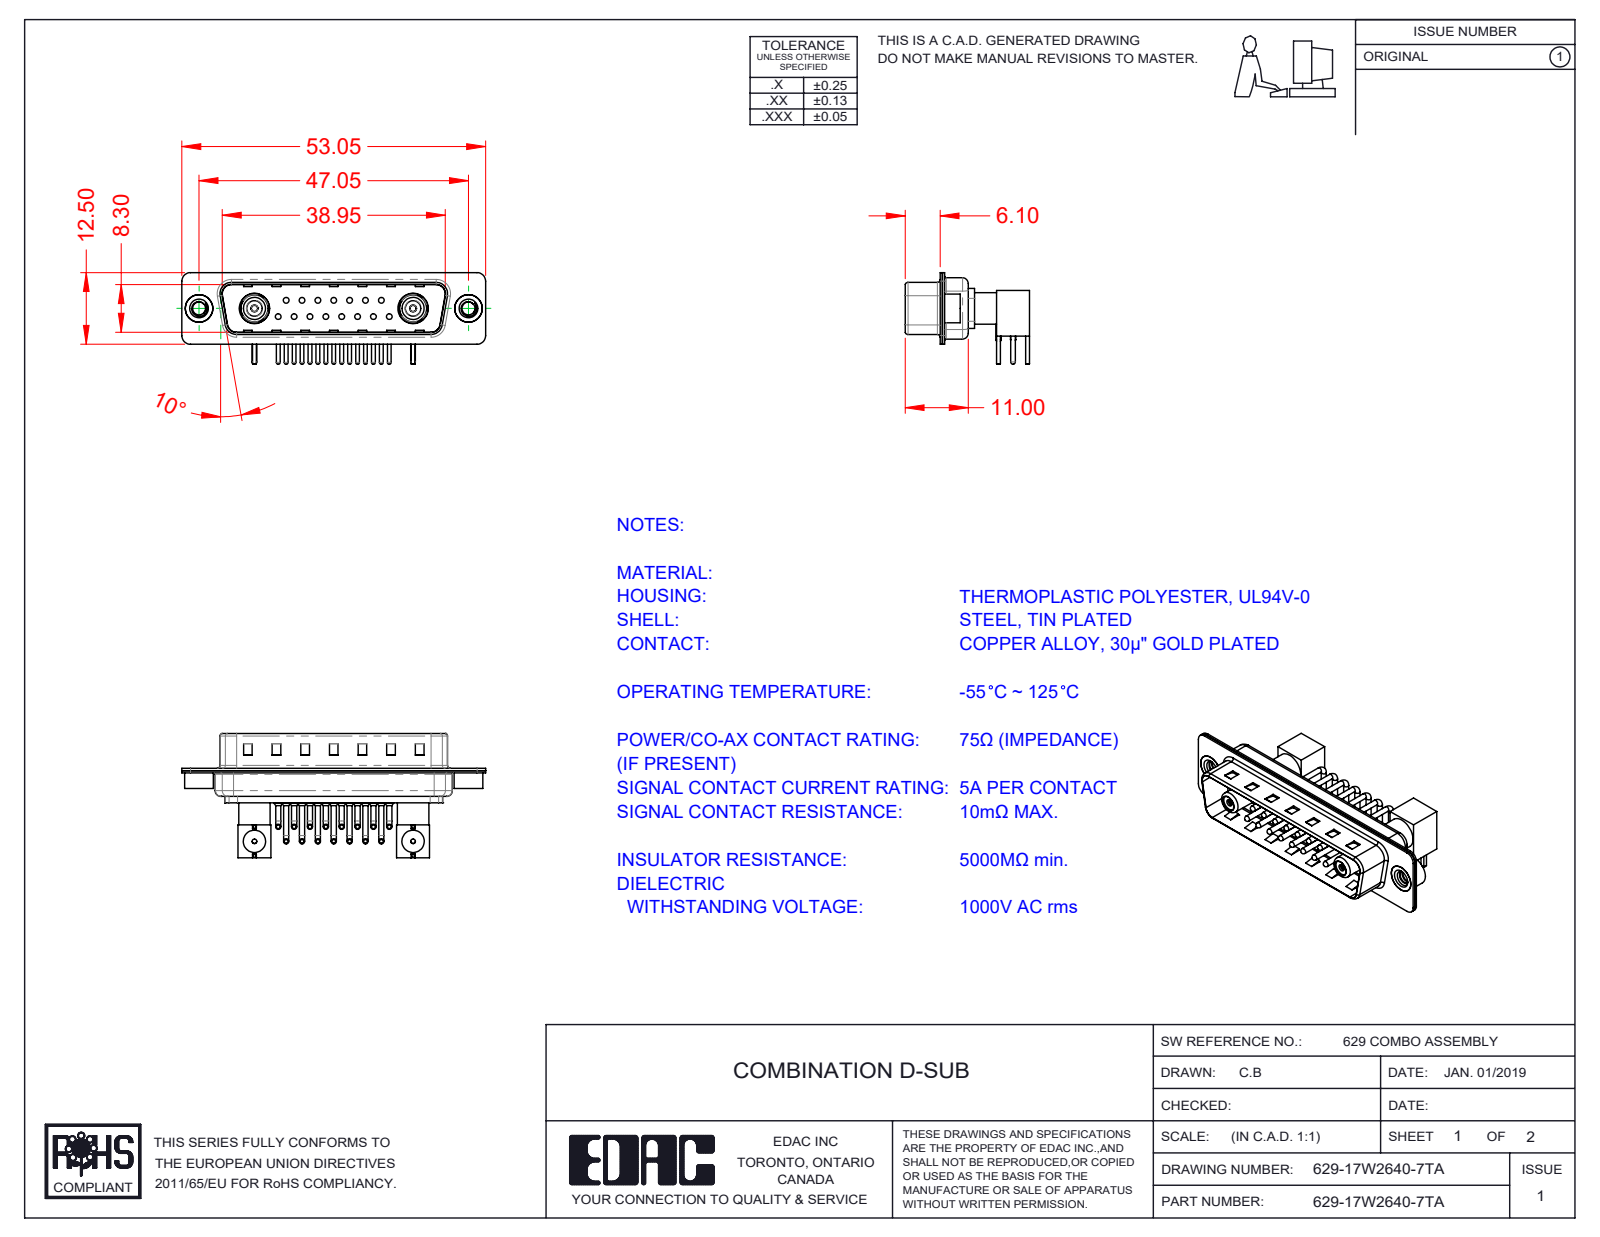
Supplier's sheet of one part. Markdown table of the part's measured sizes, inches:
| quantity | value |
| --- | --- |
| part name | RA Back Shell; Locking Collar; Co-Ax Jack Assy_RA; Insulator RA Pin (+8 more) |
| STEP written by | SolidWorks 2020 (CONFIG_CONTROL_DESIGN) |
| units | inches |
| bodies | 34 solids, 2330 faces (1245 planar, 811 cylindrical, 274 other) |
| overall size | 2.089 × 0.855 × 0.63 |
| volume | 0.208 in³ |
| surface area | 14.21 in² |
| round holes (diameter × count) | 0.063 × 17, 0.03 × 15, 0.079 × 15, 0.031 × 2, 0.043 × 2, 0.047 × 2, 0.059 × 2, 0.089 × 2, 0.098 × 2, 0.106 × 2, 0.122 × 2, 0.134 × 2 |
| round bosses / shafts (diameter × count) | 0.035 × 30, 0.059 × 15, 0.039 × 15, 0.026 × 15, 0.031 × 4, 0.217 × 2, 0.205 × 2, 0.197 × 2 |
| partial cylindrical surfaces (radius × count) | 0.059 × 16, 0.04 × 15, 0.079 × 12, 0.02 × 8, 0.063 × 8, 0.01 × 4, 0.024 × 4, 0.026 × 4 |
| main face-to-face distances | 0.016, 0.031, 0.374, 0.358, 0.343, 0.014, 0.39, 0.03, 0.047, 0.055 |
| hole center spacings | 0.124, 0.109, 0.218, 0.327, 0.198, 0.295, 0.436, 1.091 |
